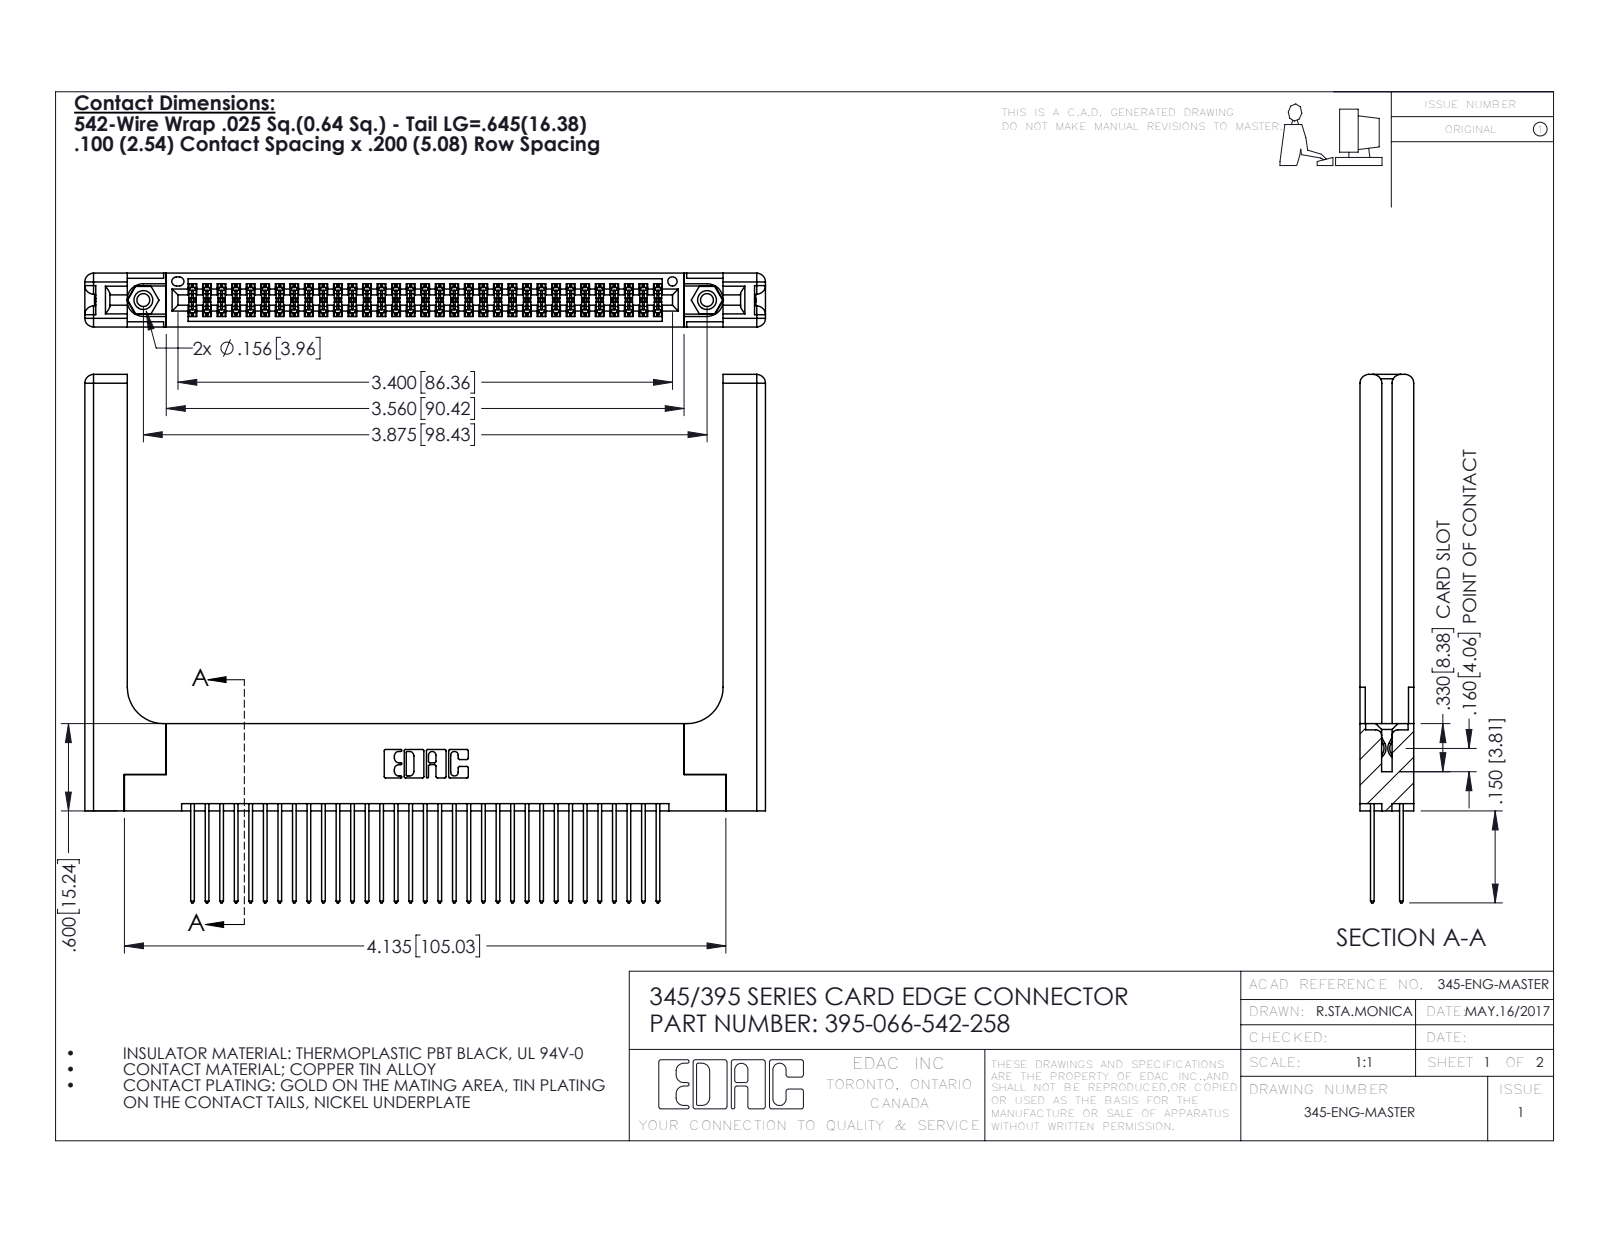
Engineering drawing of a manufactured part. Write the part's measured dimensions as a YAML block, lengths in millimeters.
part_name: "345-220-058_345-220-058; 345 Part_Flush Mounting Lugs - 0.156 Dia-TH; 395-066-542-258; 345-292-001_345-293-142 (+1 more)"
step_written_by: "SolidWorks 2016 (CONFIG_CONTROL_DESIGN)"
units: millimeters
bodies: {solids: 71, faces: 3682, planar: 2406, cylindrical: 1216, other: 60}
overall_size: [118.8, 92.3, 9.4]
volume: 20240
surface_area: 23720
round_holes:
  - {diameter: 2.3, count: 2}
  - {diameter: 3.2, count: 2}
  - {diameter: 4, count: 2}
  - {diameter: 1.6, count: 1}
round_bosses_or_shafts:
  - {diameter: 3.9, count: 2}
partial_cylinders:
  - {radius: 0.2, count: 99}
  - {radius: 0.3, count: 66}
  - {radius: 0.3, count: 22}
  - {radius: 1.5, count: 16}
  - {radius: 0.2, count: 6}
  - {radius: 0.8, count: 6}
  - {radius: 0.7, count: 3}
  - {radius: 0.4, count: 2}
face_to_face_distances: [1.8, 7.6, 9.4, 5.1, 2.5, 6.9, 0.6, 5.7, 3.8, 3.8]
hole_center_spacings: [6.9, 92.5, 98.4]
